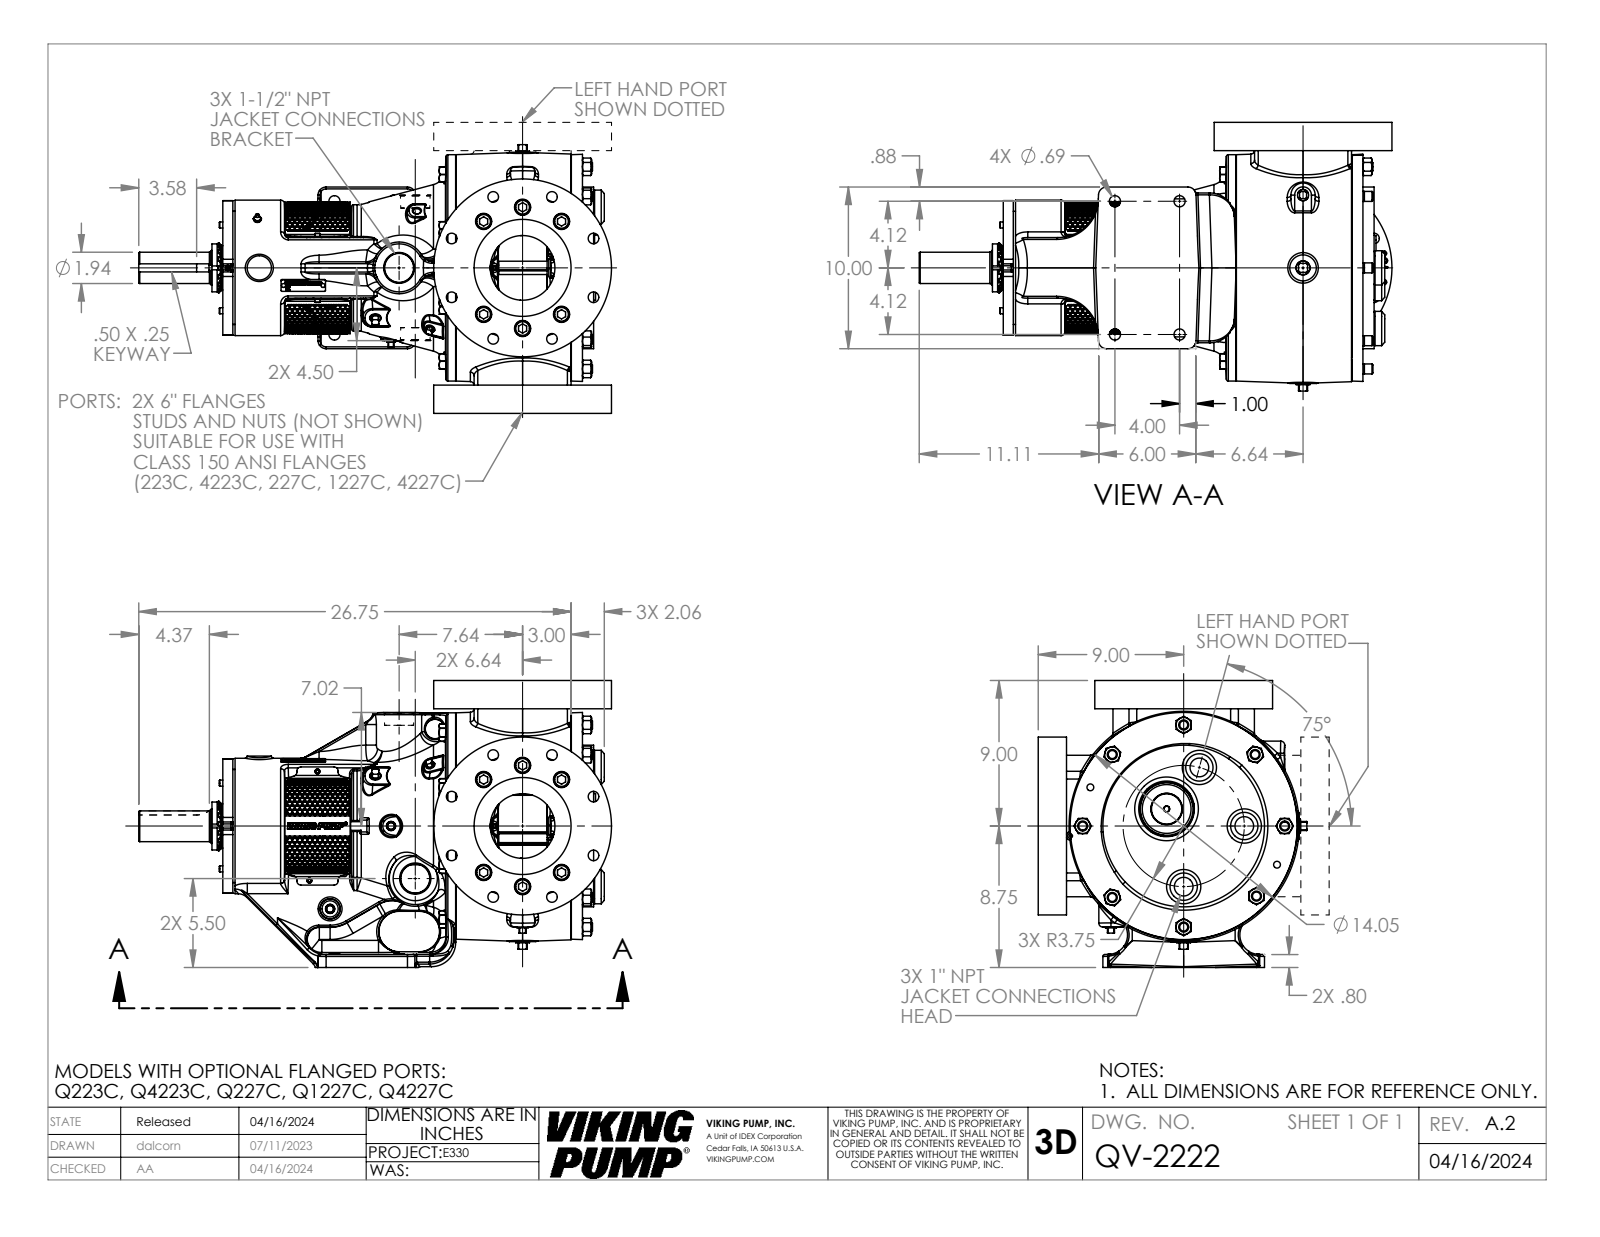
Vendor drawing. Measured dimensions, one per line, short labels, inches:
name: QV-2222
written by: SolidWorks 2022 (AUTOMOTIVE_DESIGN)
unit: in
bodies: 1 solid, 3835 faces (1352 planar, 714 cylindrical, 1769 other)
size: 29.249 × 17.75 × 16.621
volume: 2 529 in³; area: 2 354 in²
holes: 16× ⌀0.656, 12× ⌀0.656, 12× ⌀1, 9× ⌀0.25, 8× ⌀0.266, 8× ⌀1.157, 4× ⌀0.688, 3× ⌀1.156, 3× ⌀1.85, 2× ⌀0.159, 2× ⌀0.313, 2× ⌀0.33
bosses: 12× ⌀0.937, 11× ⌀0.625, 8× ⌀0.617, 3× ⌀2.12, 3× ⌀1.75, 3× ⌀0.312, 3× ⌀0.19, 2× ⌀11
rounds: 52× R0.12, 18× R0.015, 18× R0.092, 18× R0.25, 16× R0.07, 16× R0.75, 14× R0.5, 10× R0.24
face distances: 1.75, 0.691, 17.75, 16, 3.75, 22.254, 22.944, 18.504, 19.194, 7.909
hole spacings: 3.75, 2.079, 3.133, 3.635, 4.75, 5.932, 6.718, 8.43
